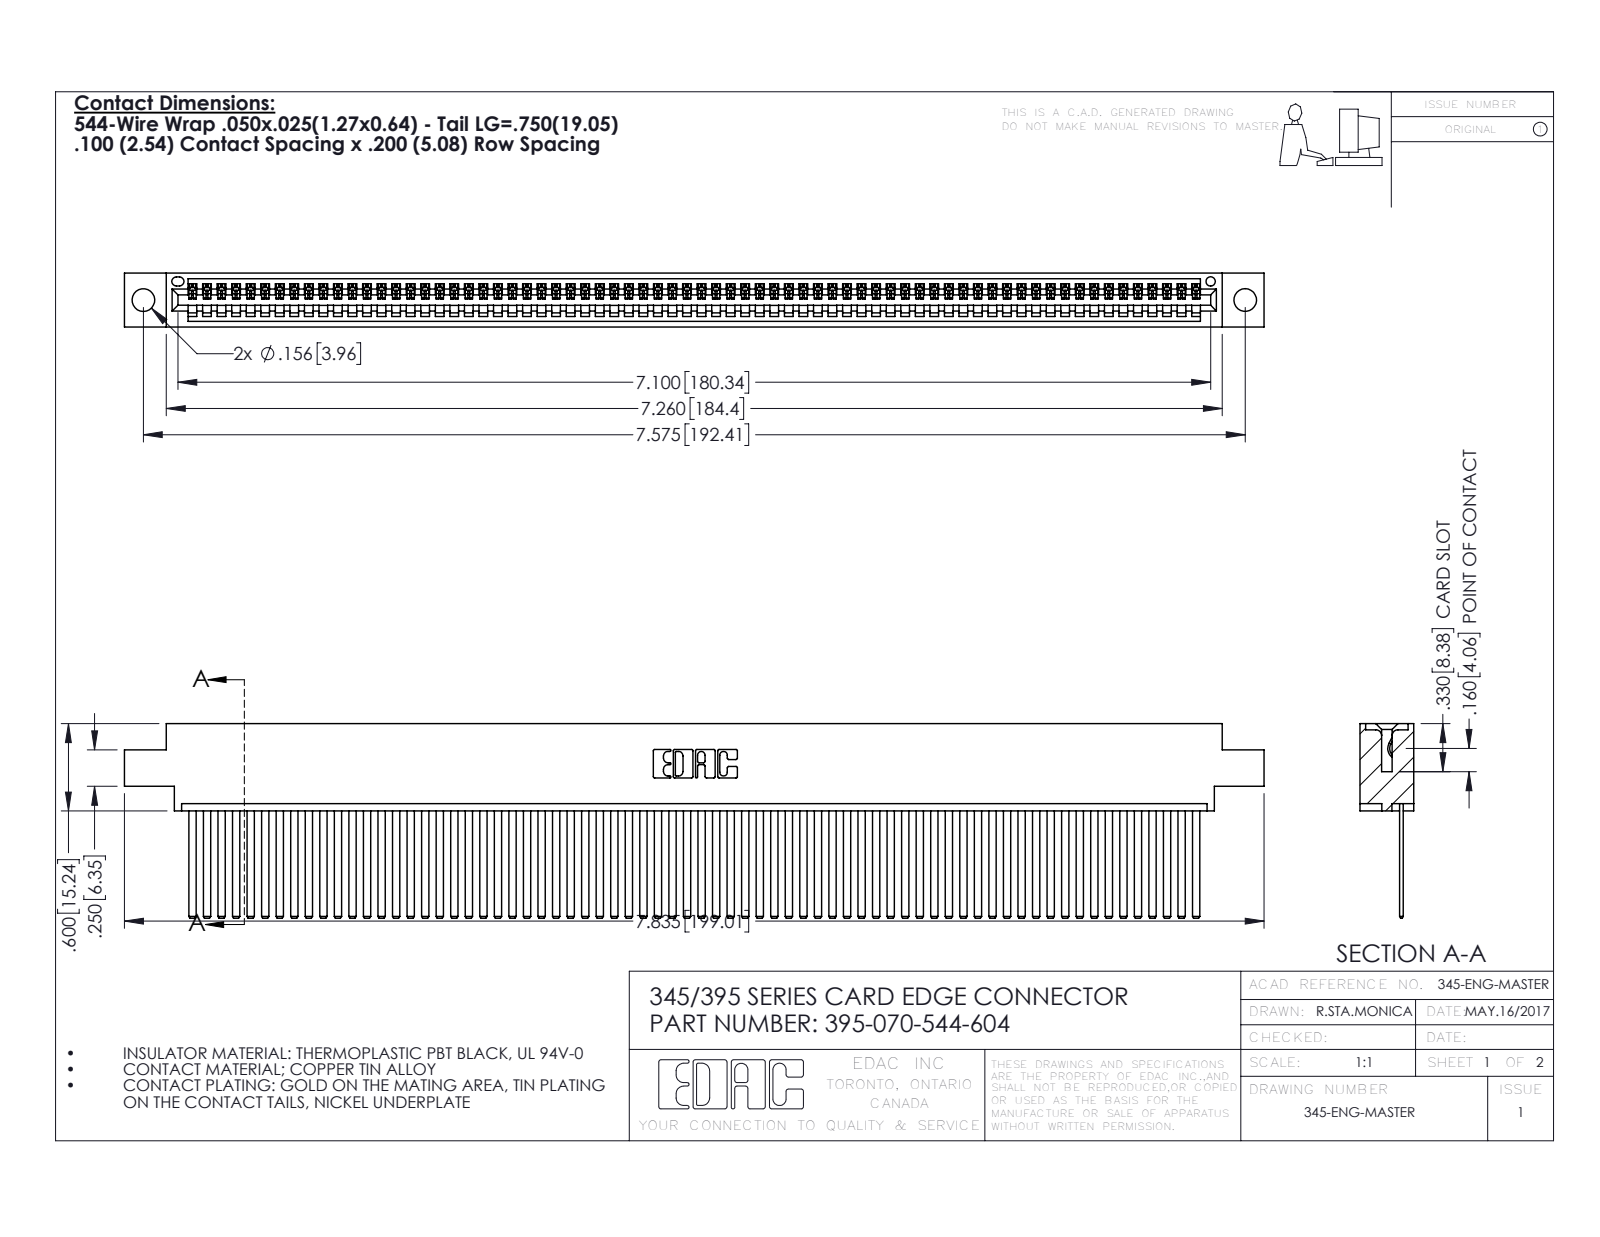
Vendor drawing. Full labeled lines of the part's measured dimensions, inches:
Part name (STEP PRODUCT): 345 Part_0.170 Offset - 0.156 Dia-TH; 345-292-001_345-293-144; 395-070-544-604
STEP written by: SolidWorks 2016 (CONFIG_CONTROL_DESIGN)
Units: inches
Bodies: 71 solids, 3770 faces (2604 planar, 1166 cylindrical, 0 other)
Overall size (bounding box): 7.835 × 1.337 × 0.37
Volume: 1.205 in³ · Surface area: 44.92 in²
Round holes (diameter × count): ⌀0.156 ×2, ⌀0.064 ×1
Partial cylindrical surfaces — rounded edges, fillets, slot ends (radius × count): R0.006 ×140, R0.01 ×22, R0.007 ×6, R0.031 ×6, R0.026 ×3, R0.031 ×2, R0.04 ×2, R0.014 ×1
Main face-to-face distances: 0.072, 0.298, 0.025, 0.098, 0.272, 0.37, 0.2, 0.225, 0.175, 0.149
Hole centre spacings: 0.27, 7.339, 7.575
